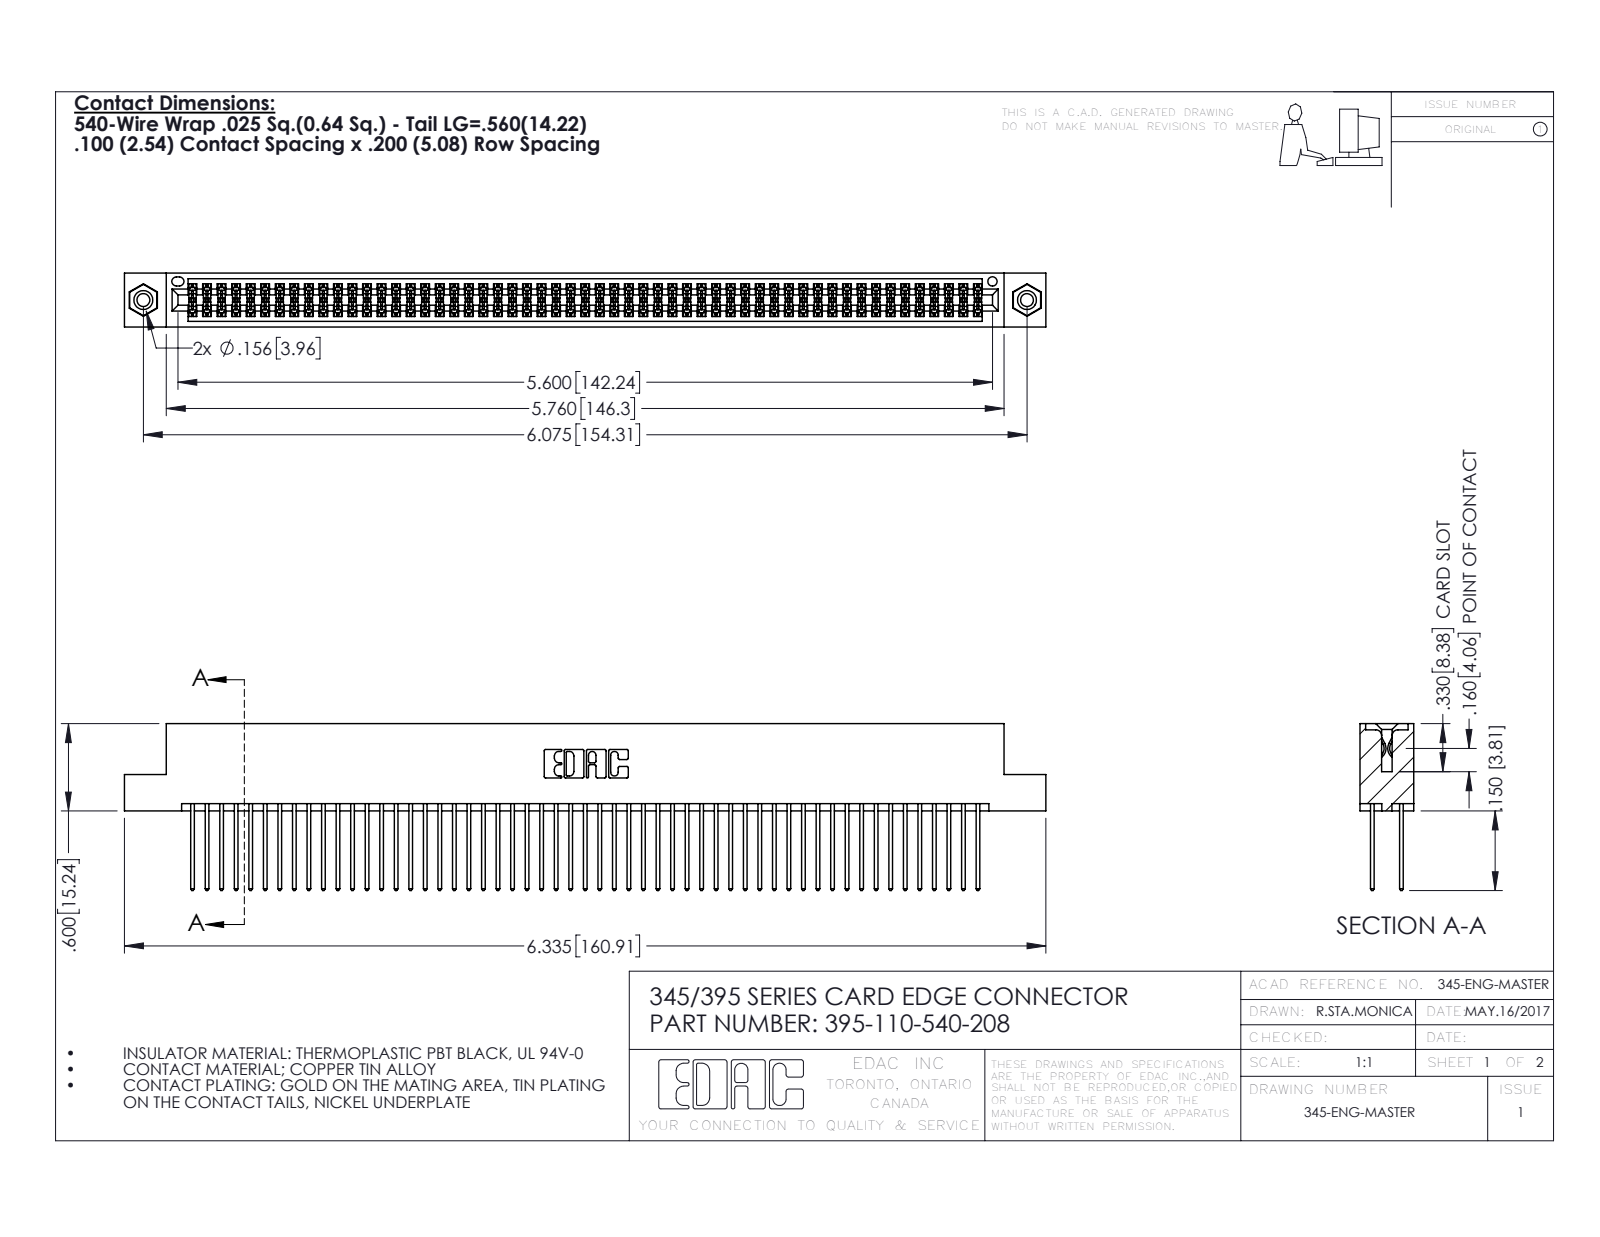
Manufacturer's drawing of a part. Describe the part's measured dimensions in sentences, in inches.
The part is named "345-250-001_345-250-003-102; 345-292-001_345-293-140; 345 Part_Flush Mounting Lugs - 0.156 Dia-TI; 395-110-540-208". Its 3-D file was written by "SolidWorks 2016 (CONFIG_CONTROL_DESIGN)". It is 113 solids with 5686 faces: 3742 planar, 1928 cylindrical and 16 other. Overall it measures 6.335 by 1.147 by 0.37 inches. Its volume is 0.986 cubic inches and its surface area 40.44 square inches. Round holes: 2 of diameter 0.089, 2 of diameter 0.125, 2 of diameter 0.156, 1 of diameter 0.064. Round bosses or shafts: 2 of diameter 0.155. Partial cylindrical surfaces (rounded edges, fillets, slot ends): 165 of radius 0.006, 110 of radius 0.01, 22 of radius 0.01, 6 of radius 0.007, 6 of radius 0.031, 3 of radius 0.026, 2 of radius 0.014, 2 of radius 0.019. The main face-to-face distances are 0.072, 0.298, 0.2, 0.098, 0.272, 0.025, 0.37, 0.225, 0.175, 0.149. The hole center spacings are 0.27, 5.839, 6.075.
